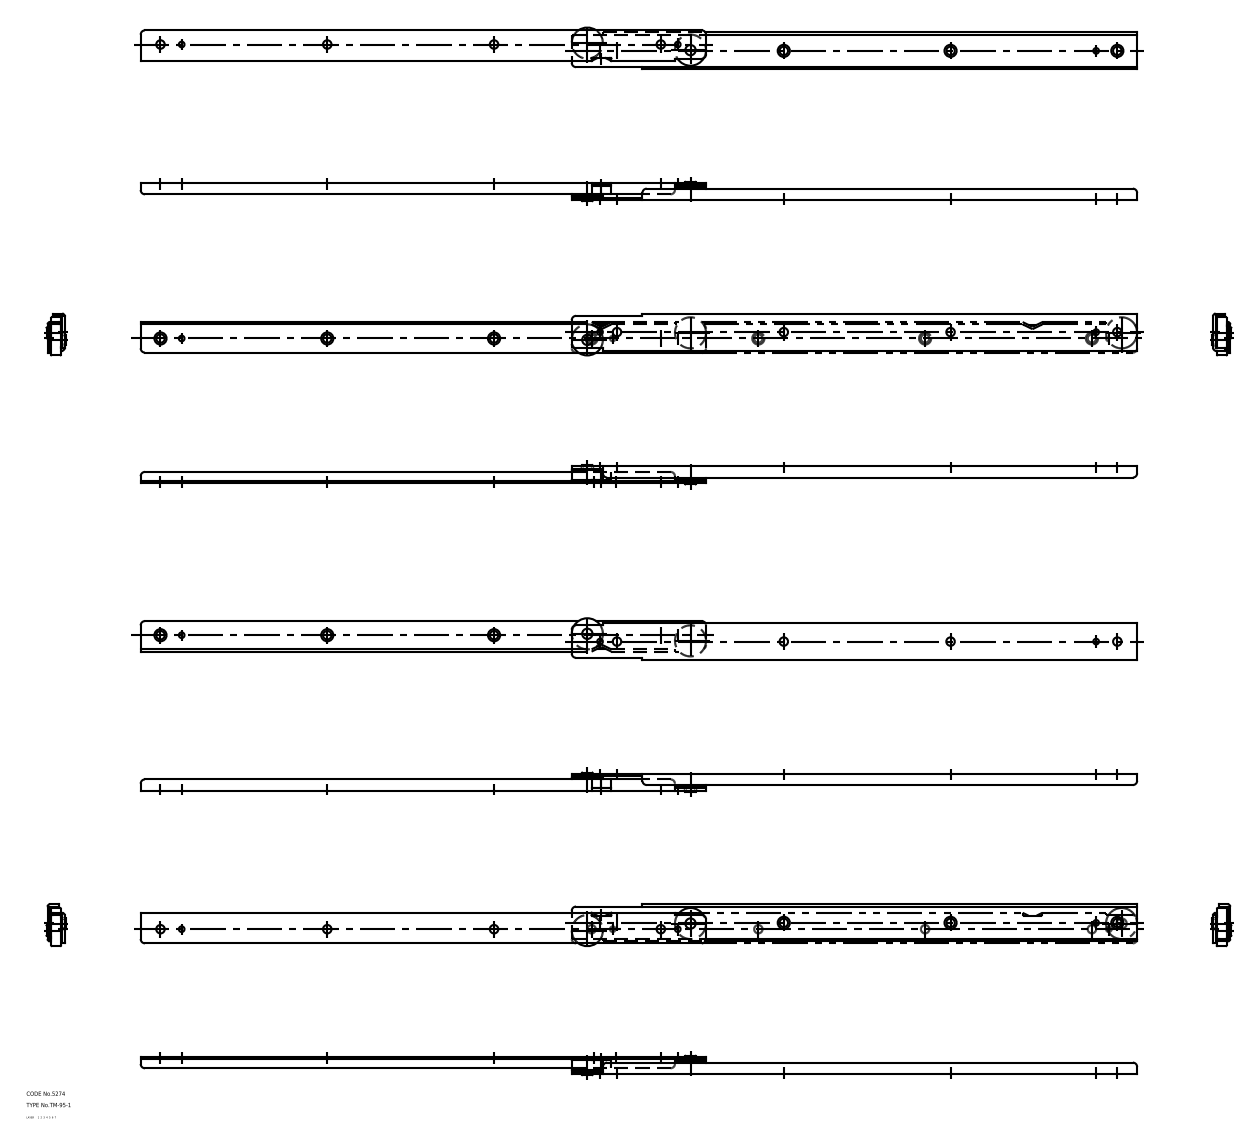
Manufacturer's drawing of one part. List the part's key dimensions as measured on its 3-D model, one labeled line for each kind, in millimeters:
Part name (STEP PRODUCT): roller; member_B; member_A; TM_95_1_7212_36
STEP written by: CADfix (AUTOMOTIVE_DESIGN)
Units: millimetres
Bodies: 4 solids, 117 faces (0 planar, 0 cylindrical, 117 other)
Overall size (bounding box): 705 × 29.6 × 13.4
Volume: 45 865 mm³ · Surface area: 56 268 mm²
